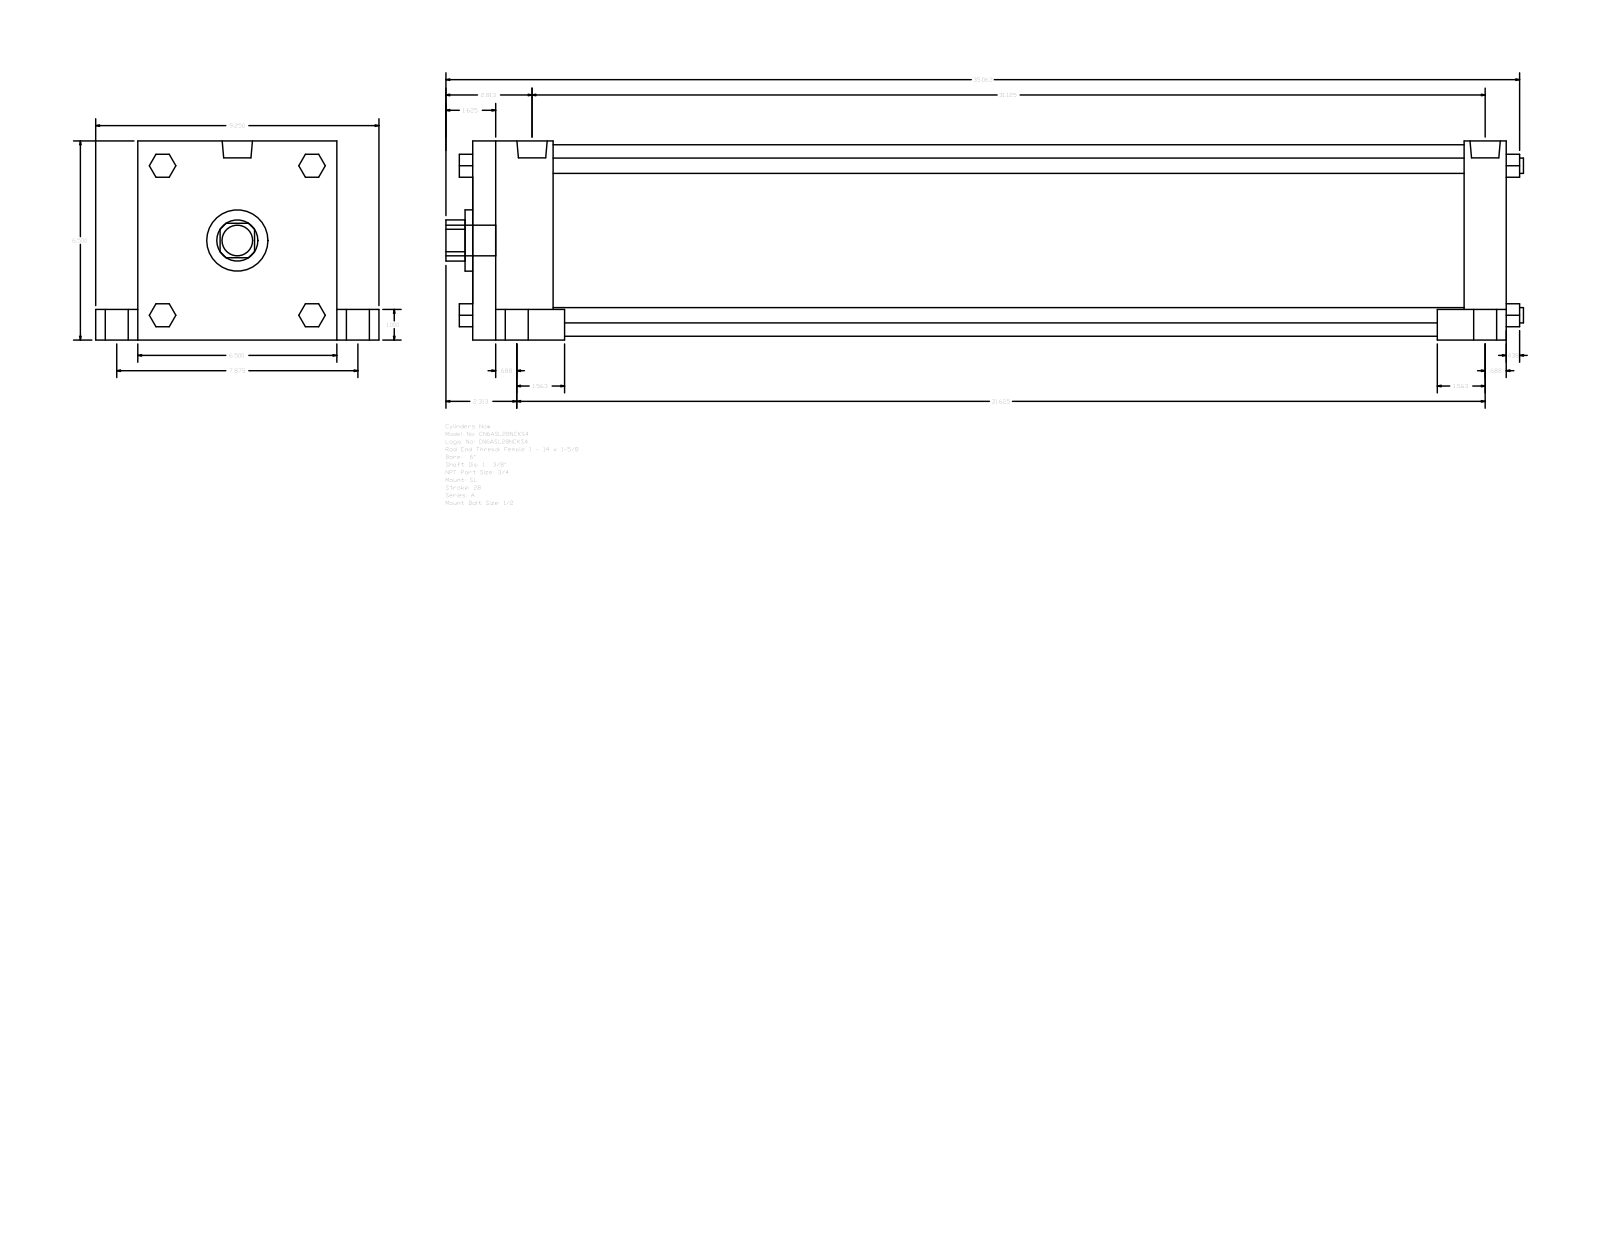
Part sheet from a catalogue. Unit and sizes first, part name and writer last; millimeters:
Units: millimetres
Overall size (bounding box): 893.76 × 234.95 × 165.1
Round holes (diameter × count): ⌀34.92 ×1, ⌀50.8 ×1, ⌀158.75 ×1
Round bosses / shafts (diameter × count): ⌀25.4 ×5, ⌀19.05 ×4, ⌀15.08 ×4, ⌀12.7 ×4, ⌀25.12 ×2
Partial cylindrical surfaces — rounded edges, fillets, slot ends (radius × count): R17.06 ×1
Main face-to-face distances: 165.1, 857.25, 66.67, 790.58, 822.32, 755.65, 34.93, 25.4, 139.7, 34.92
Bodies: 0 solids, 150 faces (114 planar, 36 cylindrical, 0 other)
Part name (STEP PRODUCT): A_SL__0600_1.375
STEP written by: GSSL Pune (CONFIG_CONTROL_DESIGN)
